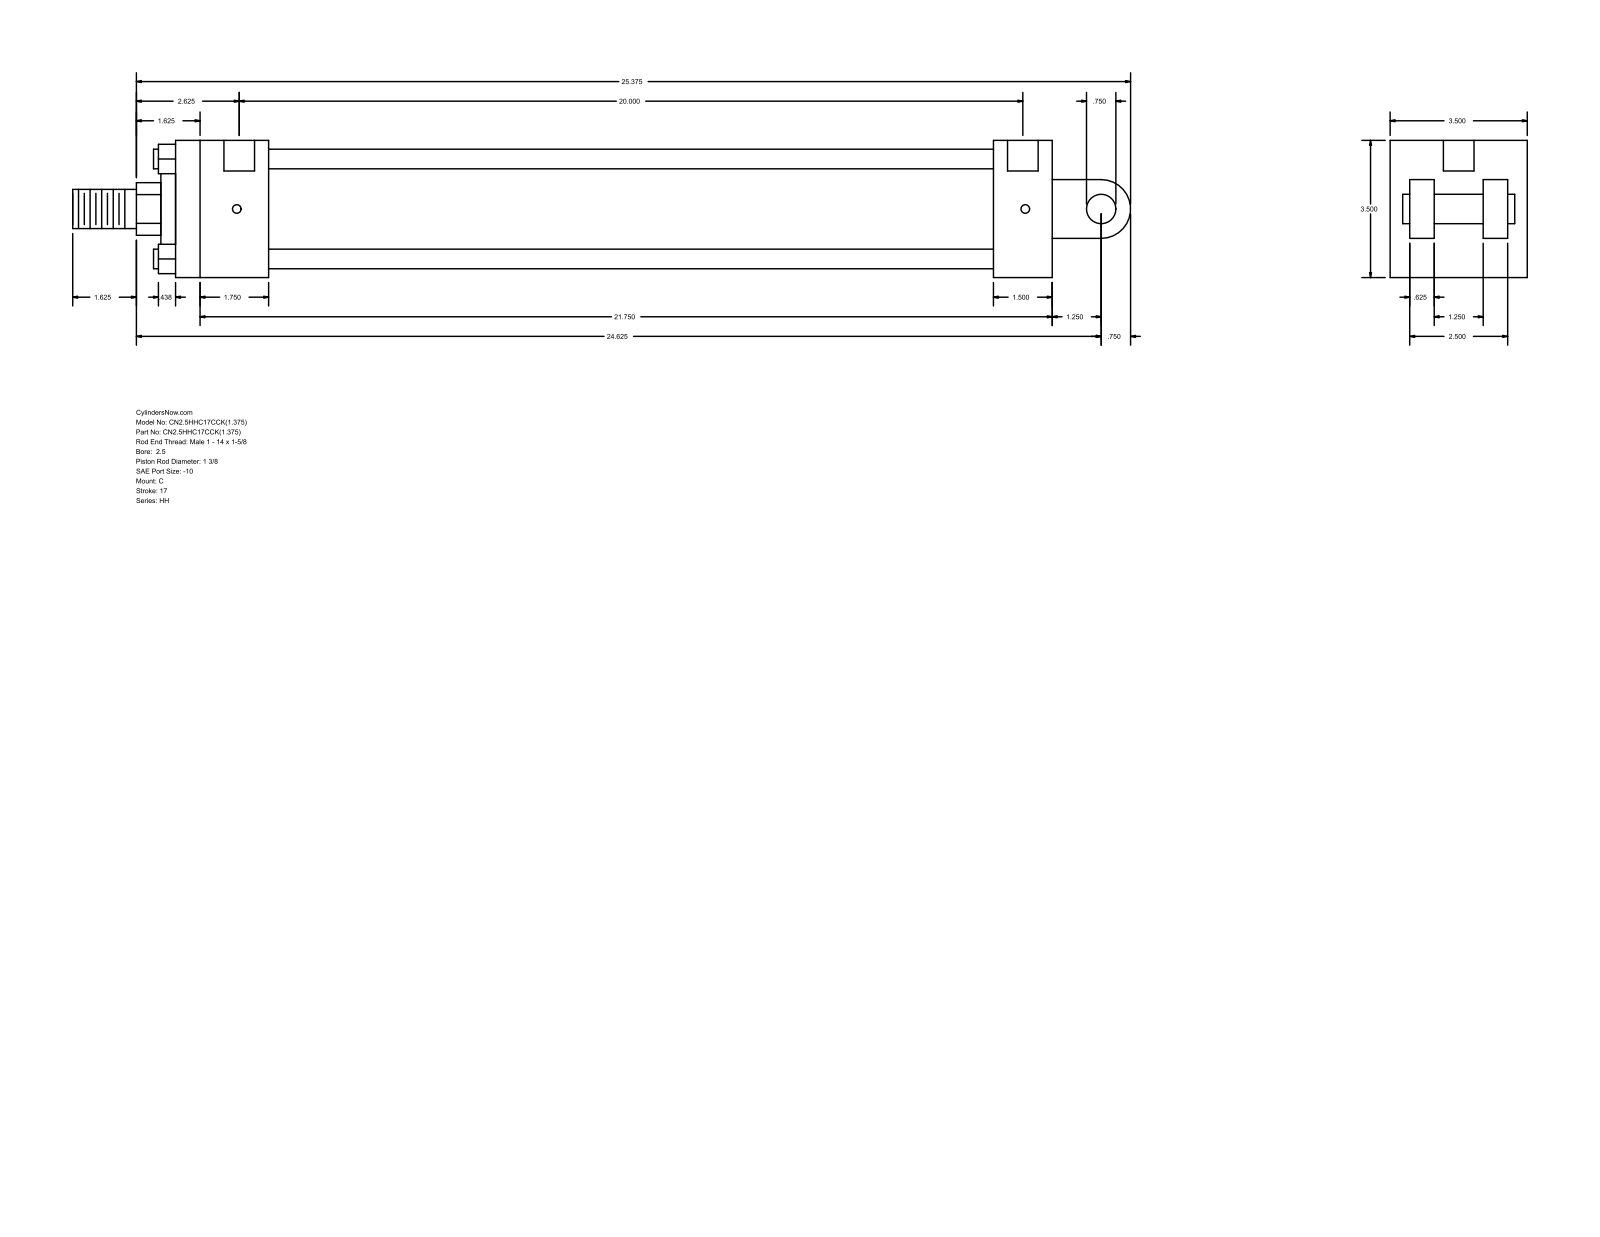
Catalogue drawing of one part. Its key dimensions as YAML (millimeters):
part_name: "HH_C__0250_1.375"
step_written_by: "GSSL Pune (CONFIG_CONTROL_DESIGN)"
units: millimeters
bodies: {solids: 0, faces: 99, planar: 70, cylindrical: 29, other: 0}
overall_size: [685.8, 88.9, 88.9]
round_holes:
  - {diameter: 5.56, count: 4}
  - {diameter: 19.84, count: 2}
round_bosses_or_shafts:
  - {diameter: 12.7, count: 4}
  - {diameter: 73.03, count: 1}
  - {diameter: 50.8, count: 1}
  - {diameter: 34.92, count: 1}
  - {diameter: 25.4, count: 1}
  - {diameter: 19.05, count: 1}
partial_cylinders:
  - {radius: 17.06, count: 1}
  - {radius: 19.05, count: 1}
face_to_face_distances: [88.9, 568.33, 63.5, 12.7, 530.22, 38.11, 60.32, 469.9, 508.01, 28.57]
hole_center_spacings: [511.17, 1.58, 1.59, 508, 509.58, 509.59]
